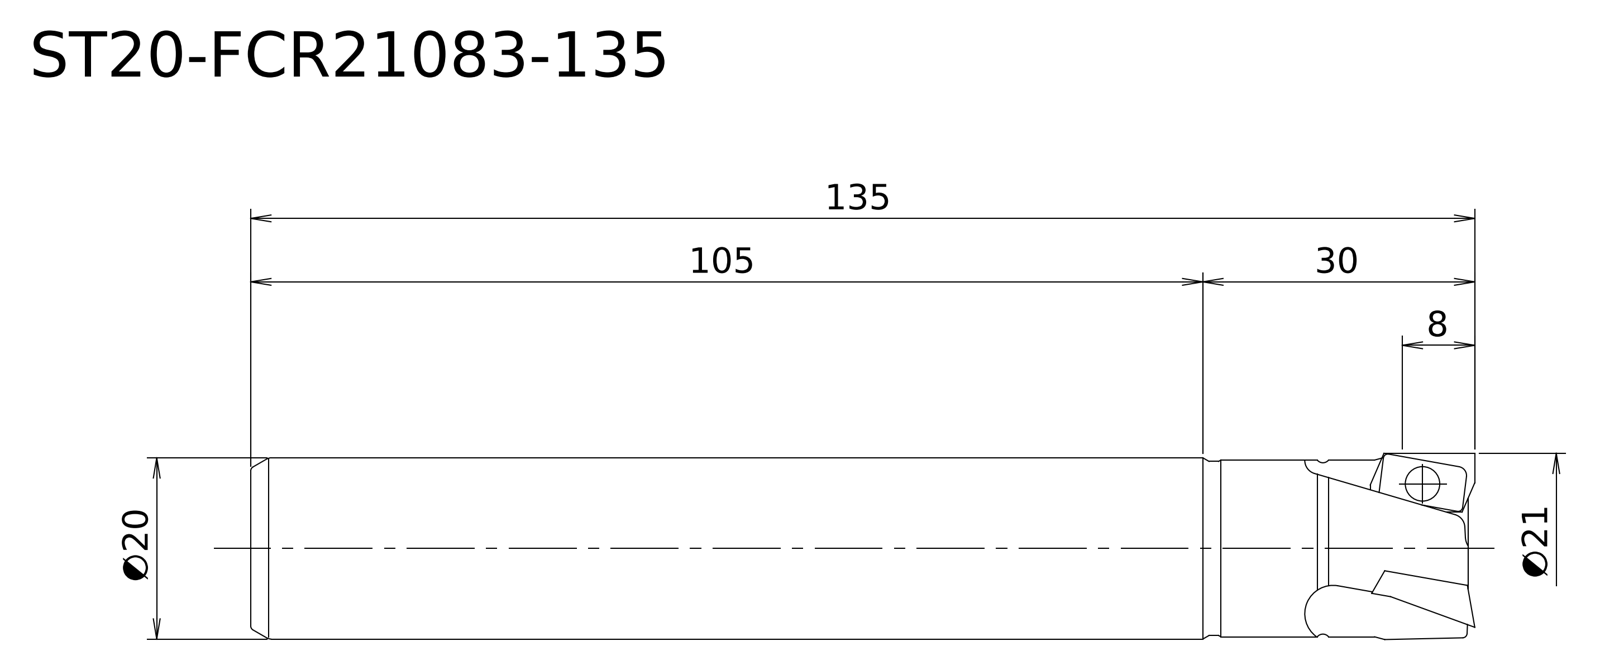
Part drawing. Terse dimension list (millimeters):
written by: Kubotek KeyCreator V8.5.1 (14335) (CONFIG_CONTROL_DESIGN)
unit: mm
bodies: 1 solid, 7 faces (2 planar, 3 cylindrical, 2 other)
size: 135 × 21 × 21
volume: 42 435 mm³; area: 9 180 mm²
bosses: 1× ⌀21, 1× ⌀20, 1× ⌀19.5
face distances: 135
